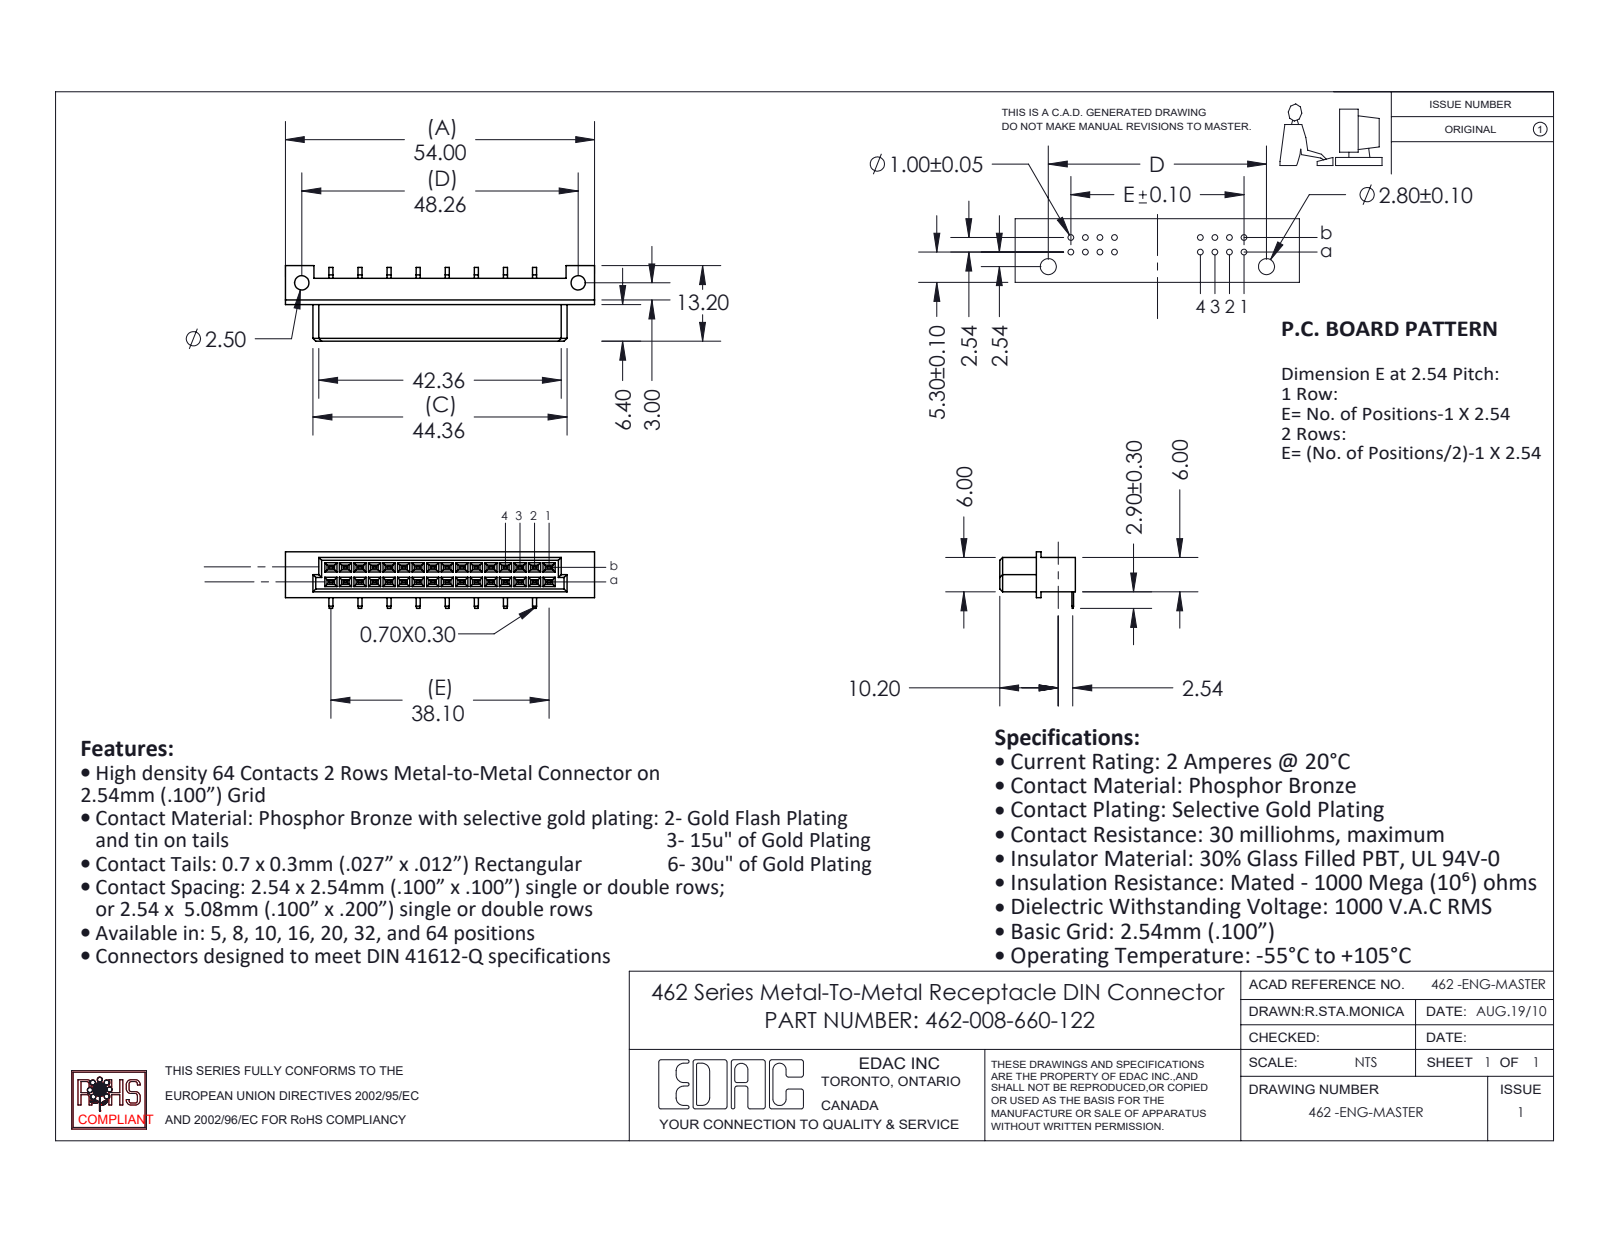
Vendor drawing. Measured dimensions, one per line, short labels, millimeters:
name: 462-008-660-122; 462 Part_32; 462-290-1
written by: SolidWorks 2020 (CONFIG_CONTROL_DESIGN)
unit: mm
bodies: 9 solids, 563 faces (543 planar, 20 cylindrical, 0 other)
size: 54 × 13.2 × 9.9
volume: 3 056 mm³; area: 3 476 mm²
holes: 2× ⌀2.5
rounds: 1× R1.02, 1× R1.32
face distances: 6, 2.54, 0.81, 4.6, 1.32, 2.13, 3.86, 4.67, 3.35, 4.68
hole spacings: 48.26
